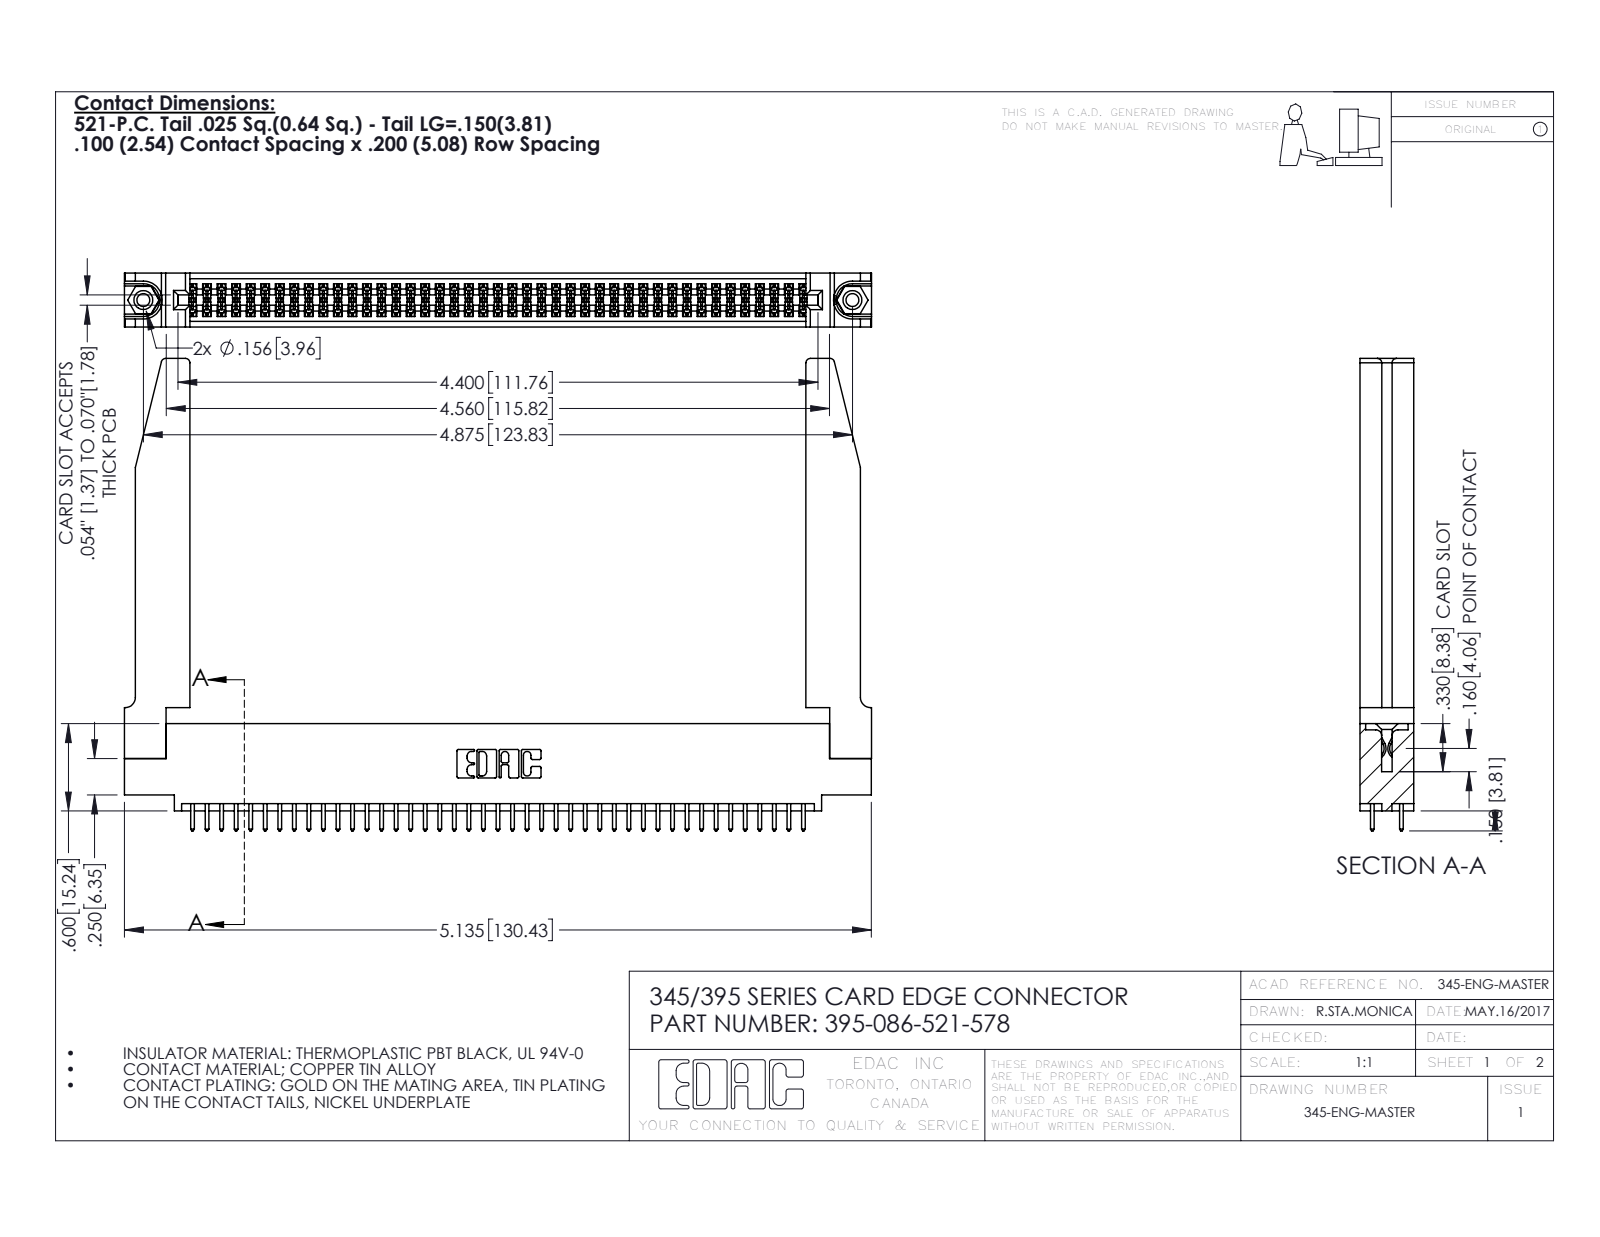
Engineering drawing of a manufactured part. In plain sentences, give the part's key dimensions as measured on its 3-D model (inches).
The part is named "345-292-001_345-293-121; 345-220-078_345-220-078; 395-086-521-578; 345-250-001_345-250-001-102 (+1 more)". Its 3-D file was written by "SolidWorks 2016 (CONFIG_CONTROL_DESIGN)". It is 91 solids with 4664 faces: 3064 planar, 1548 cylindrical and 52 other. Overall it measures 5.136 by 3.247 by 0.37 inches. Its volume is 1.241 cubic inches and its surface area 39.23 square inches. Round holes: 2 of diameter 0.089, 2 of diameter 0.125, 2 of diameter 0.156, 1 of diameter 0.064. Round bosses or shafts: 2 of diameter 0.155. Partial cylindrical surfaces (rounded edges, fillets, slot ends): 129 of radius 0.006, 86 of radius 0.01, 22 of radius 0.01, 8 of radius 0.03, 6 of radius 0.007, 6 of radius 0.031, 3 of radius 0.026, 2 of radius 0.014. The main face-to-face distances are 0.072, 0.37, 0.298, 0.2, 0.098, 0.272, 0.025, 0.225, 0.175, 0.148. The hole center spacings are 0.27, 4.639, 4.875.
